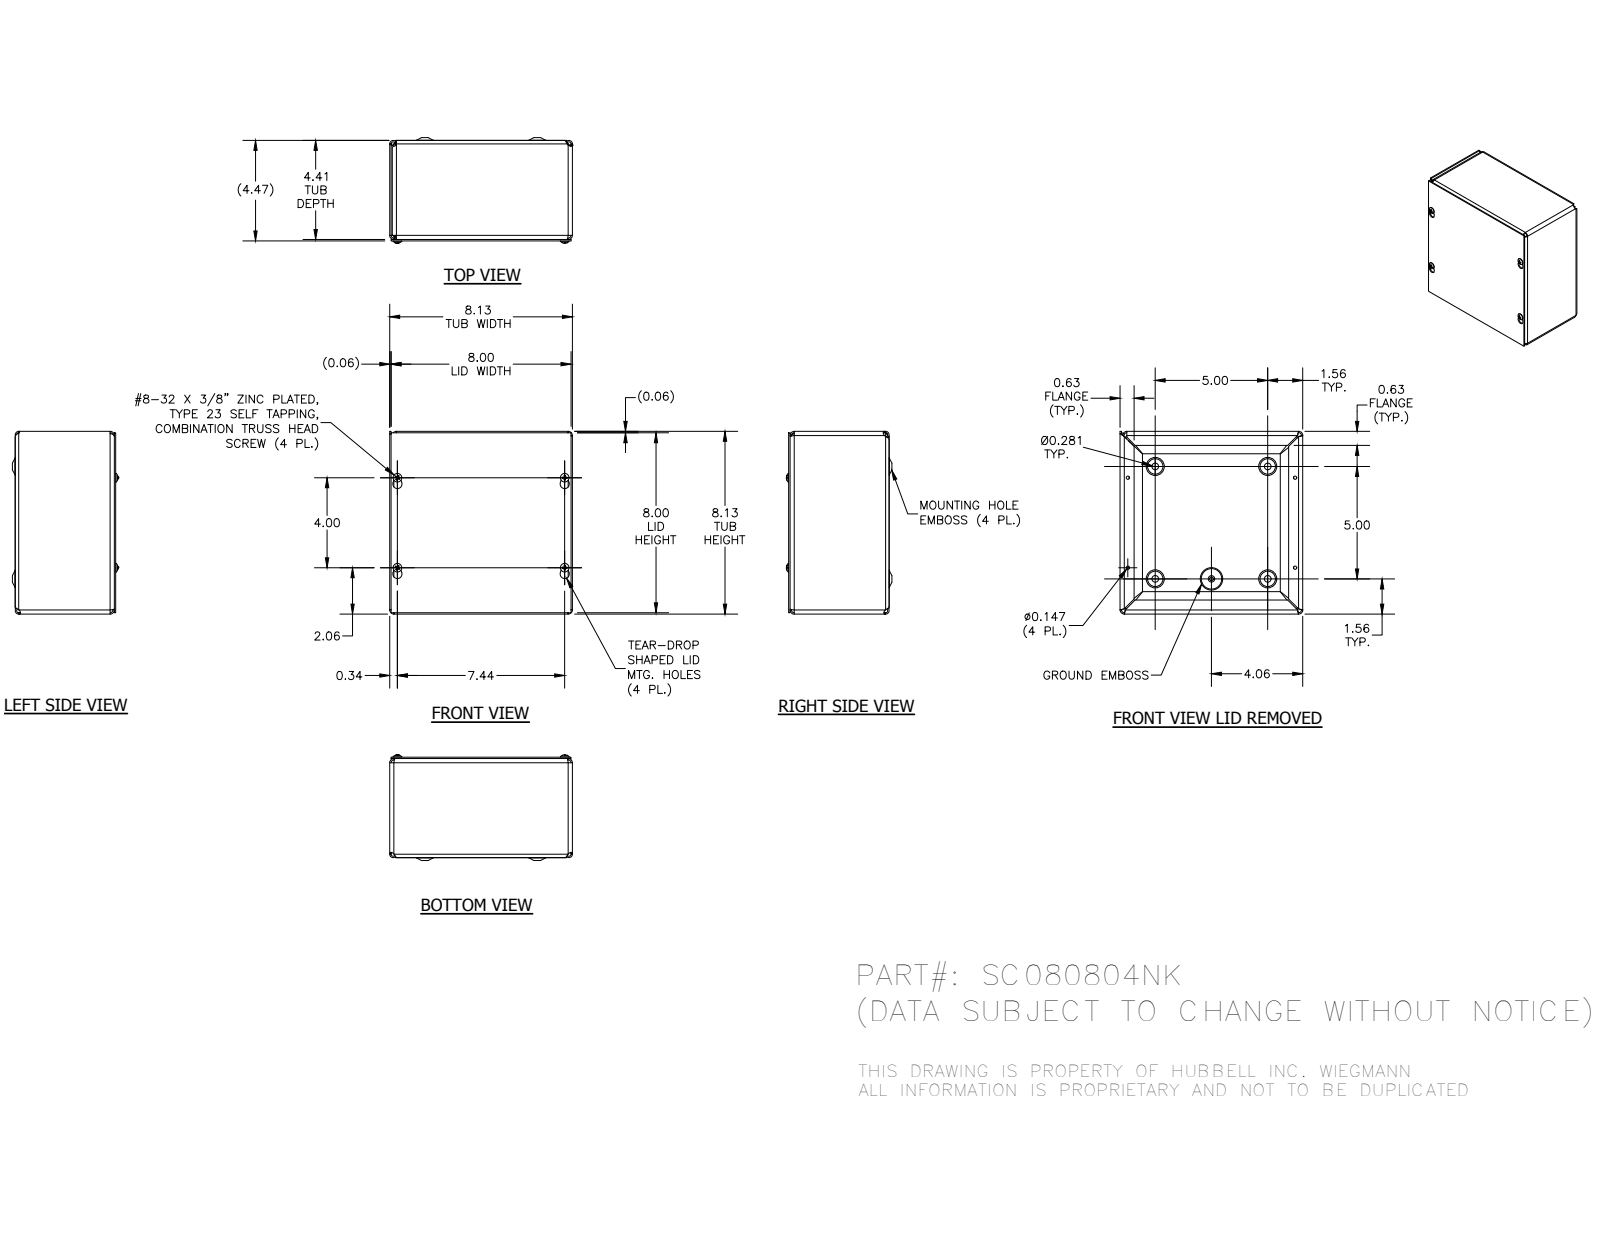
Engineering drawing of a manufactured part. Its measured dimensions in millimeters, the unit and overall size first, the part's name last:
Units: millimetres
Overall size (bounding box): 206.38 × 206.38 × 119.2
Round holes (diameter × count): ⌀3.73 ×4, ⌀7.62 ×4, ⌀4.19 ×1
Round bosses / shafts (diameter × count): ⌀9.75 ×4, ⌀4.17 ×4, ⌀5.8 ×1
Partial cylindrical surfaces — rounded edges, fillets, slot ends (radius × count): R3.17 ×12, R4.75 ×8, R1.4 ×4, R1.57 ×4, R2.38 ×4, R2.97 ×4, R3.15 ×4, R3.96 ×4
Main face-to-face distances: 1.57, 204.8, 110.32, 111.89, 203.23, 1.59, 111.91, 113.48, 1.58, 206.37
Hole centre spacings: 118.42, 127, 33.45, 33.46, 63.5, 101.6, 141.99, 158.46
Volume: 309 537 mm³ · Surface area: 399 254 mm²
Bodies: 7 solids, 357 faces (132 planar, 67 cylindrical, 158 other)
Part name (STEP PRODUCT): SC0808BKP; SC080804NKWRA; SC0808LID; 34056 (+1 more)
STEP written by: Autodesk Inventor 2014 (AUTOMOTIVE_DESIGN)
